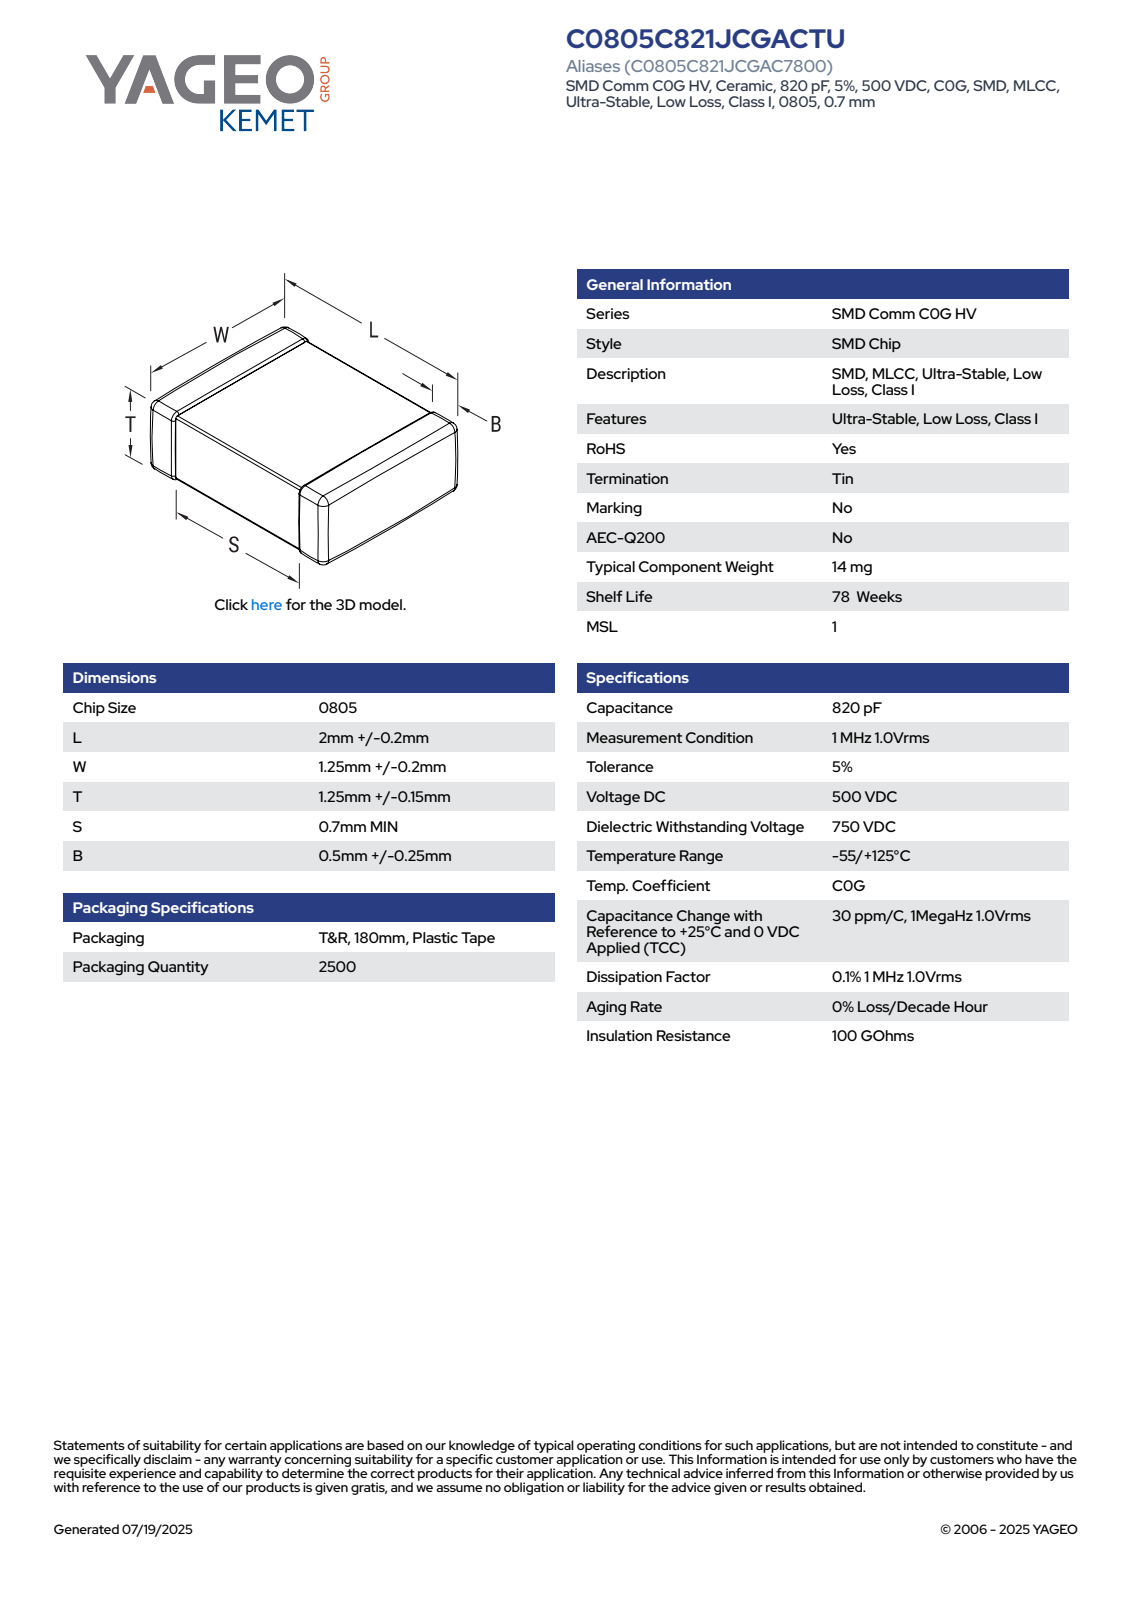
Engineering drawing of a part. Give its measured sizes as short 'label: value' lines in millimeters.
name: CCS_CCSTD_0805_L2.2W1.45T1.4B0.5
written by: SolidWorks 2014 (AUTOMOTIVE_DESIGN)
unit: mm
bodies: 4 solids, 121 faces (71 planar, 34 cylindrical, 16 other)
size: 2.2 × 1.45 × 1.4
volume: 4 mm³; area: 17 mm²
face distances: 1.37, 1.42, 2.2, 1.34, 1.39, 1.4, 1.45, 0.97, 1.23, 1.19
